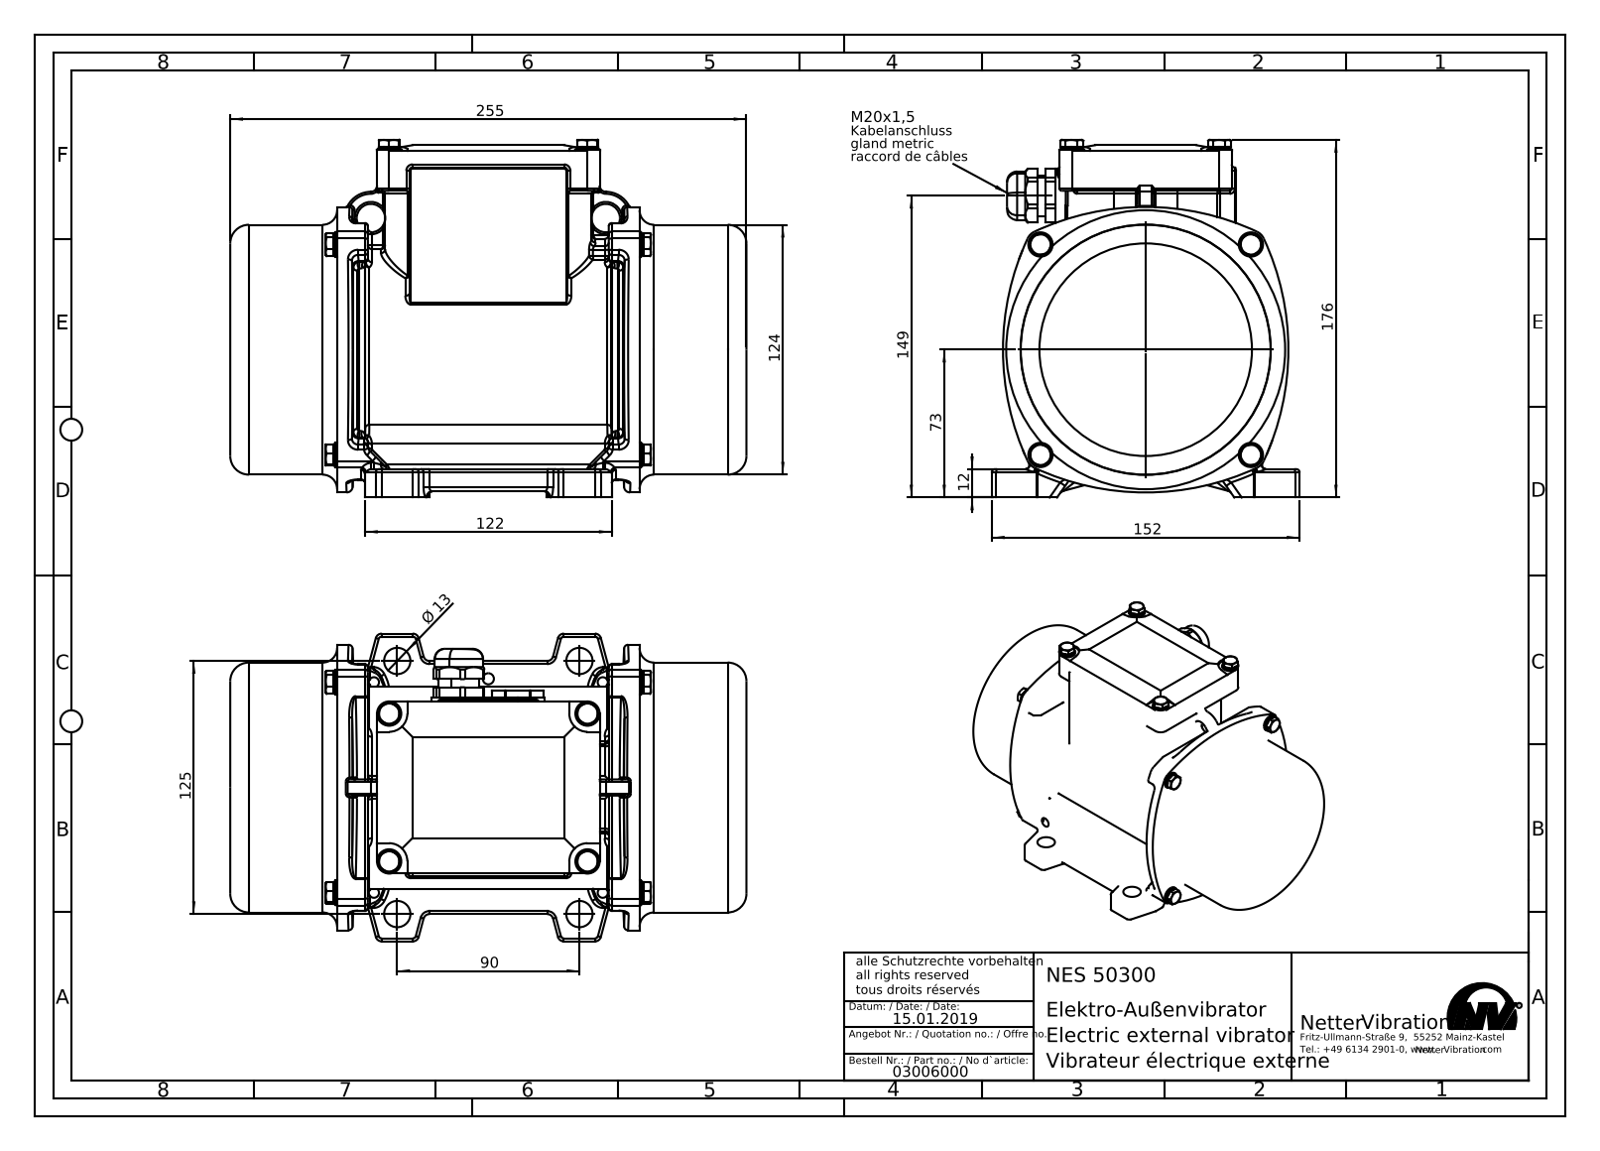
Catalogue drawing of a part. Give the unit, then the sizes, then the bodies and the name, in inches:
Units: inches
Overall size (bounding box): 10.039 × 6.953 × 5.984
Round holes (diameter × count): ⌀0.512 ×4, ⌀0.197 ×2, ⌀0.217 ×1, ⌀0.551 ×1
Round bosses / shafts (diameter × count): ⌀0.472 ×8, ⌀0.394 ×8, ⌀4.858 ×1, ⌀3.937 ×1
Partial cylindrical surfaces — rounded edges, fillets, slot ends (radius × count): R0.118 ×70, R0.079 ×53, R0.059 ×34, R0.039 ×17, R0.004 ×12, R0.02 ×12, R0.276 ×8, R0.02 ×6
Main face-to-face distances: 10.039, 0.157, 6.299, 2.079, 7.961, 0.079, 0.551, 4.508, 6.85, 2.677
Hole centre spacings: 1.805, 3.543, 4.906, 4.921, 6.064, 4.092
Volume: 198.4 in³ · Surface area: 310 in²
Bodies: 1 solid, 1704 faces (438 planar, 430 cylindrical, 836 other)
Part name (STEP PRODUCT): NES 50300 #03006000
STEP written by: SolidWorks 2015 (CONFIG_CONTROL_DESIGN)
